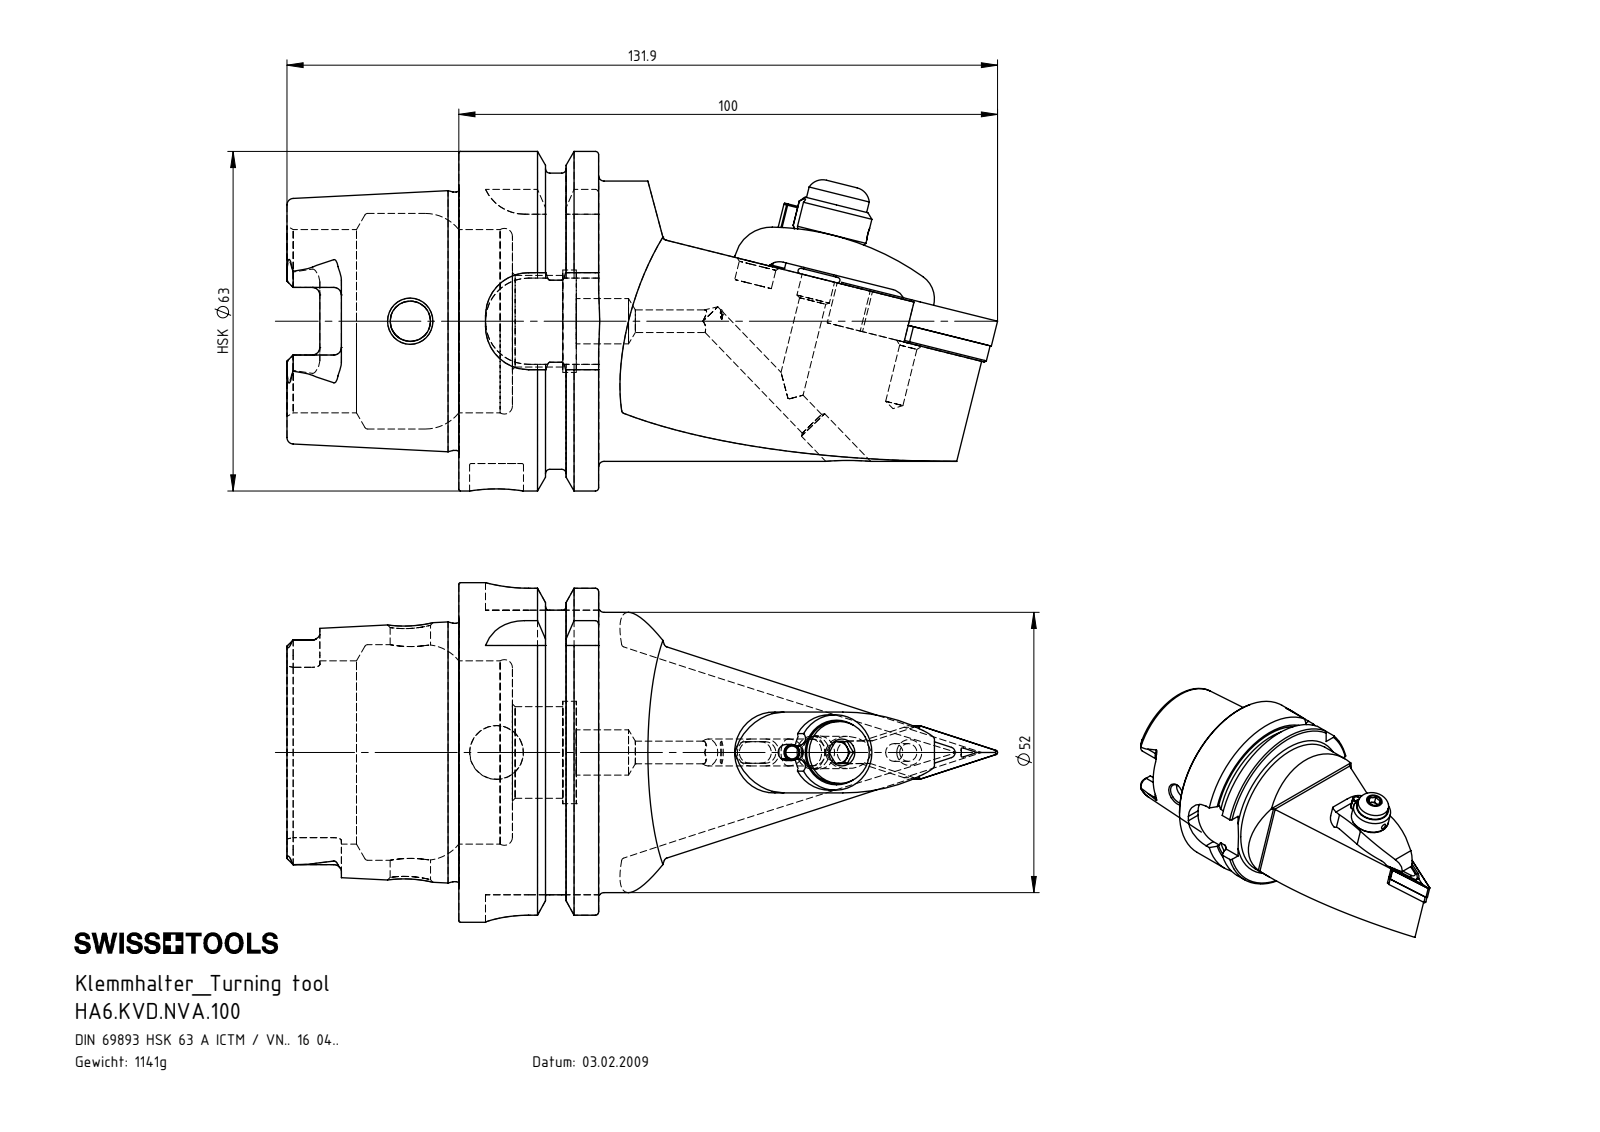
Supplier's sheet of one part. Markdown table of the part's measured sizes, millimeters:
| quantity | value |
| --- | --- |
| part name | HA6.KVD.NVA.100; WCC-ER5.102.005_A; VNMG160404; HA6-KVD.NVA.100_C (+6 more) |
| STEP written by | SolidWorks 2017 (CONFIG_CONTROL_DESIGN) |
| units | millimeters |
| bodies | 9 solids, 439 faces (124 planar, 150 cylindrical, 165 other) |
| overall size | 131.9 × 63 × 63 |
| volume | 153 510 mm³ |
| surface area | 35 410 mm² |
| round holes (diameter × count) | 2 × 3, 4.2 × 2, 5 × 2, 7 × 2, 2.4 × 1, 3 × 1, 3.3 × 1, 3.8 × 1, 4.95 × 1, 6.2 × 1, 6.9 × 1, 7.5 × 1 |
| round bosses / shafts (diameter × count) | 4 × 2, 3 × 2, 63 × 1, 54.95 × 1, 52 × 1, 47.94 × 1, 14 × 1, 11.5 × 1 |
| partial cylindrical surfaces (radius × count) | 0.34 × 6, 0.59 × 6, 1.4 × 6, 0.4 × 4, 8 × 4, 1.5 × 3, 0.5 × 2, 0.8 × 2 |
| main face-to-face distances | 8.94, 25.95, 16, 9.95, 31.9, 41.85, 57.85, 52.8, 21.8, 4.46 |
| hole center spacings | 27.32, 8.02, 8.2, 19.12, 19.3, 19.31, 8.01 |
